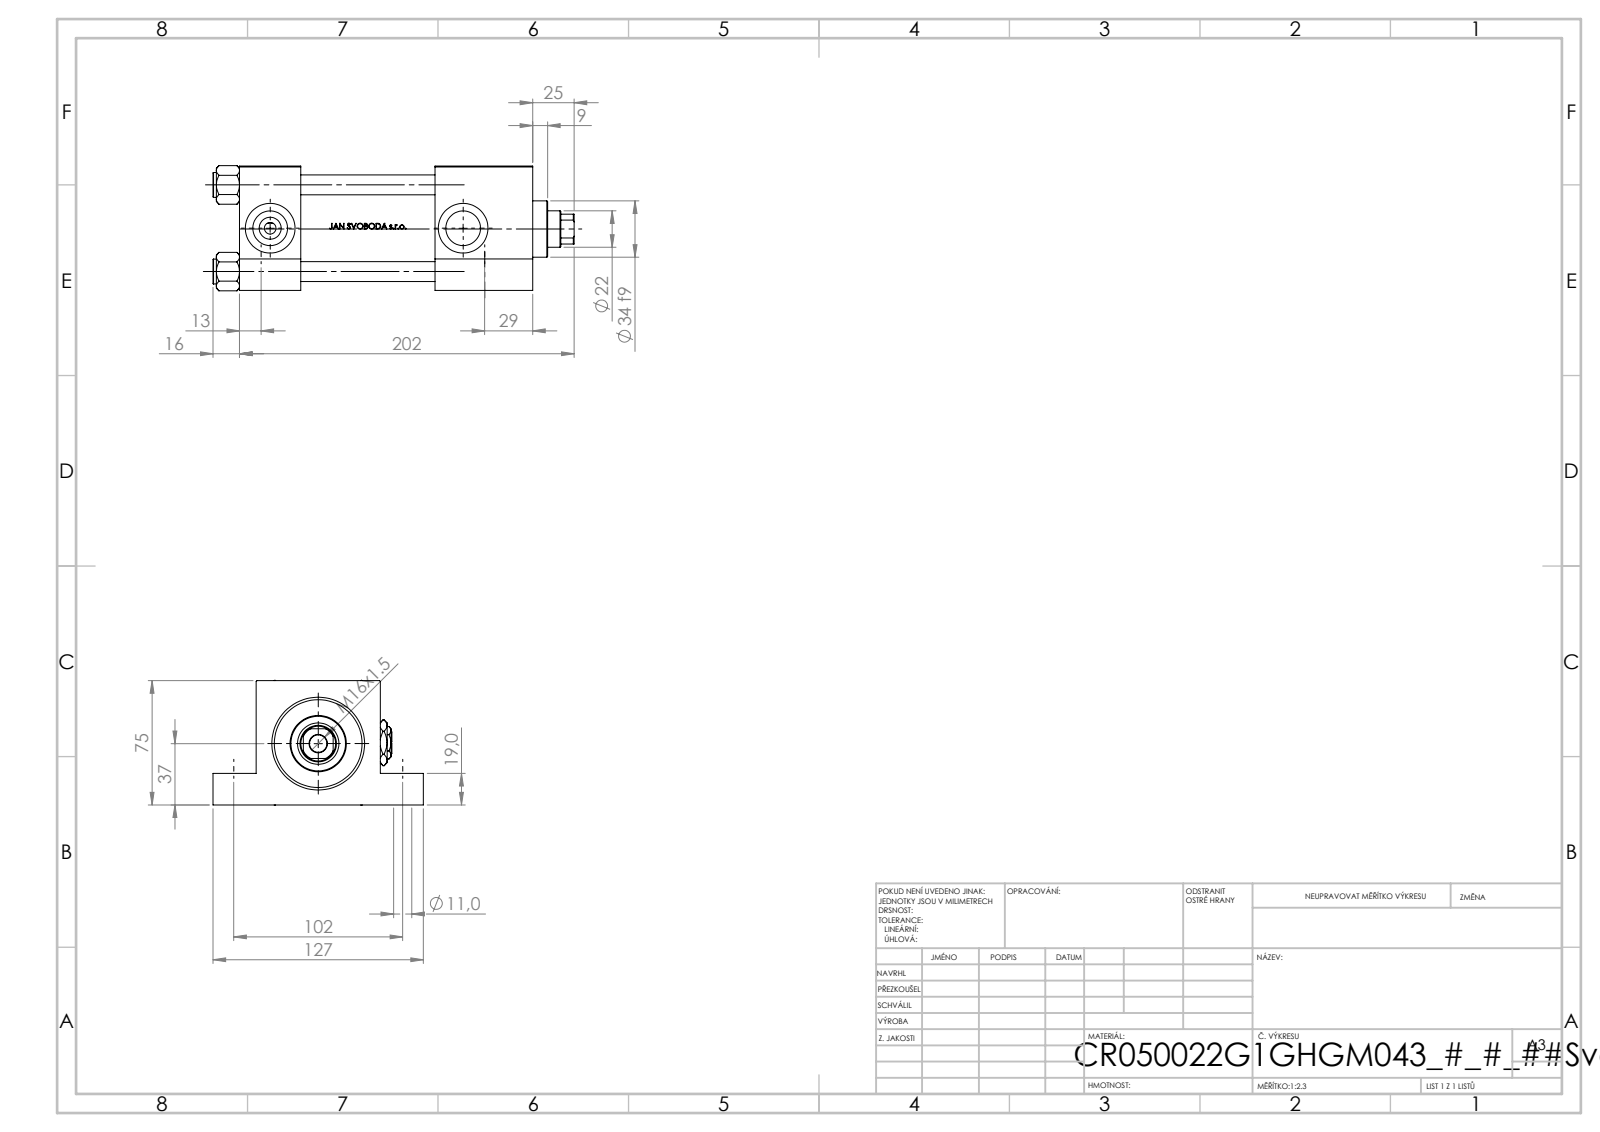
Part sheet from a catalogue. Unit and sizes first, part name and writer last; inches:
Units: inches
Overall size (bounding box): 8.583 × 5 × 2.974
Round holes (diameter × count): ⌀0.433 ×4, ⌀0.472 ×4, ⌀0.276 ×2, ⌀0.825 ×2, ⌀1.181 ×2, ⌀0.413 ×1, ⌀0.866 ×1, ⌀0.984 ×1, ⌀1.614 ×1, ⌀1.969 ×1, ⌀2.087 ×1
Round bosses / shafts (diameter × count): ⌀0.591 ×4, ⌀2.205 ×1, ⌀1.339 ×1
Partial cylindrical surfaces — rounded edges, fillets, slot ends (radius × count): R0.413 ×1
Main face-to-face distances: 2.953, 1.457, 6.969, 5.512, 2.205, 0.748, 4.646, 3.189, 2.323, 1.024
Hole centre spacings: 2.059, 1.442, 1.47, 2.912, 4.016, 5.315, 6.661, 4.587
Volume: 47.78 in³ · Surface area: 269.7 in²
Bodies: 12 solids, 1134 faces (454 planar, 128 cylindrical, 552 other)
Part name (STEP PRODUCT): V215CR_G_Body; V215CR_VCP_G; NUT_M5_G; V215_VC_A (+2 more)
STEP written by: SolidWorks 2019 (CONFIG_CONTROL_DESIGN)
